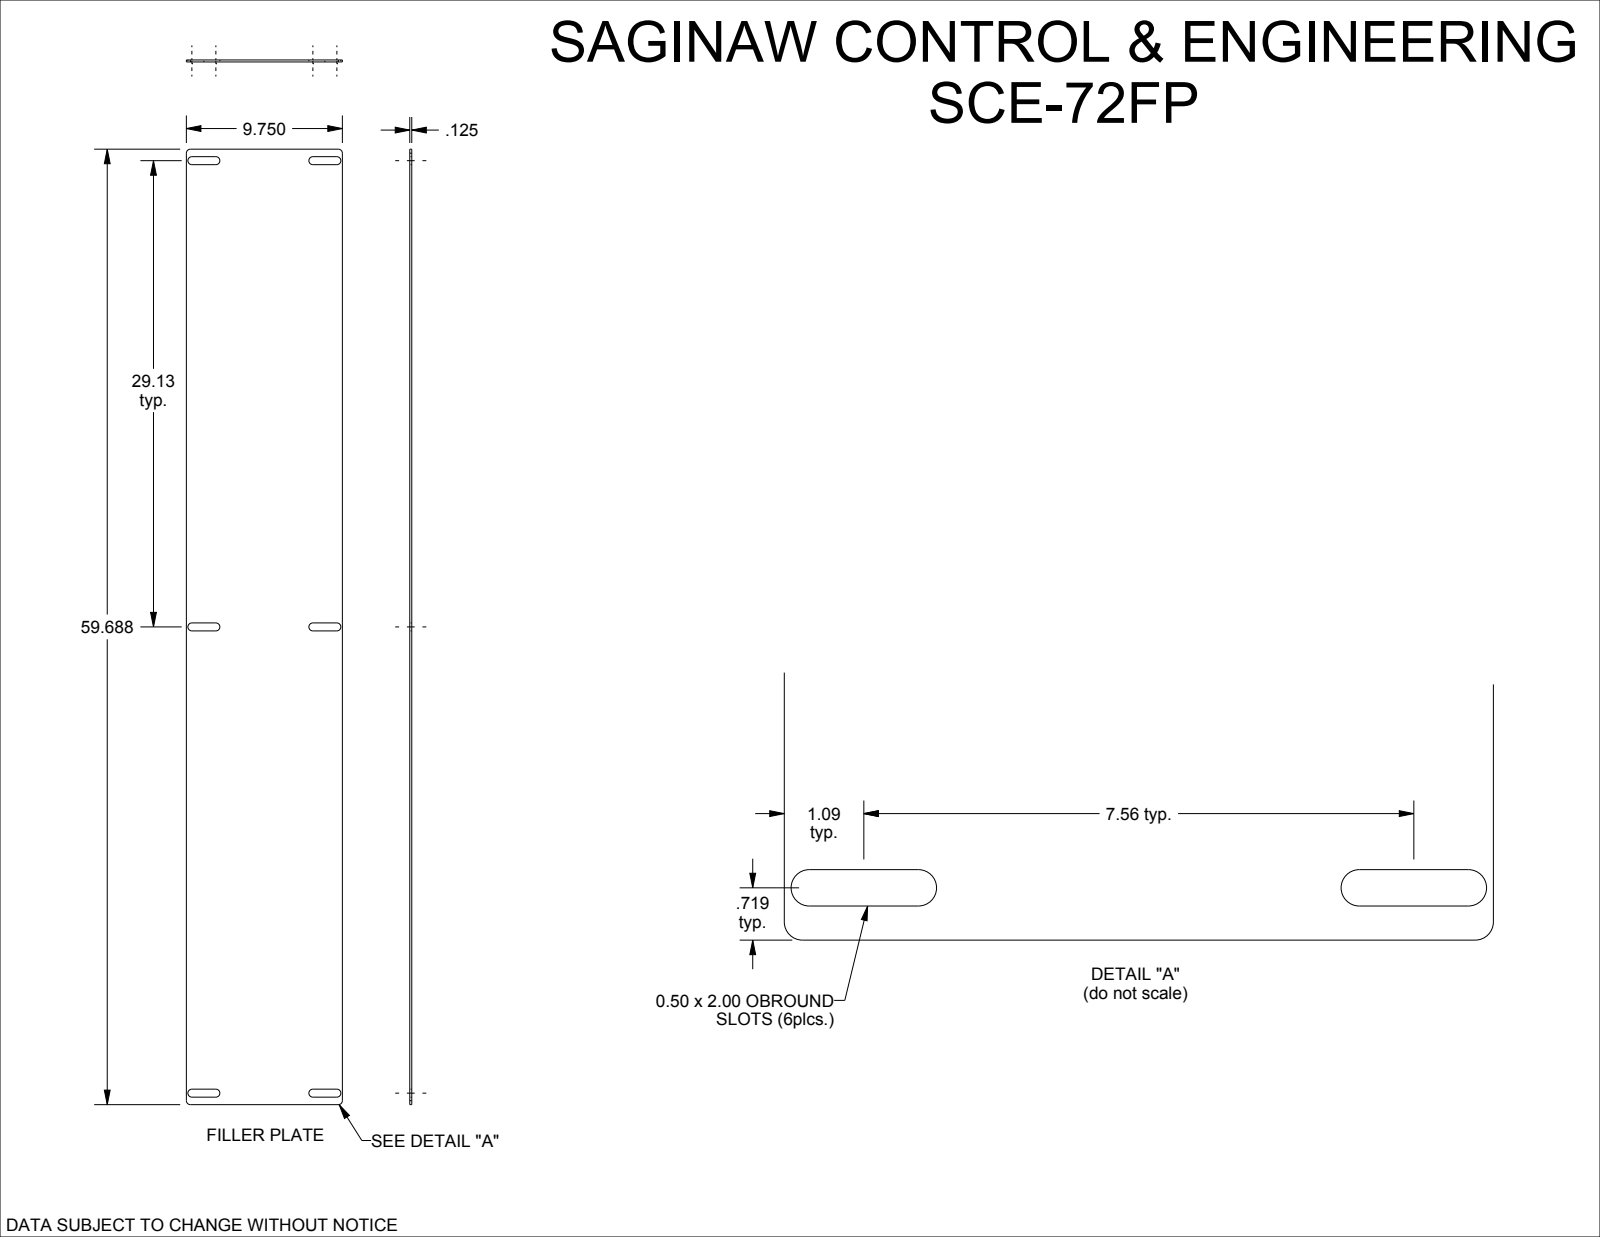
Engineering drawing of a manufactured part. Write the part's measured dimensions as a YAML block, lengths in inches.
part_name: "SCE-72FP"
step_written_by: "SolidWorks 2023 (AUTOMOTIVE_DESIGN)"
units: inches
bodies: {solids: 1, faces: 46, planar: 30, cylindrical: 16, other: 0}
overall_size: [59.687, 9.75, 0.125]
volume: 72.03
surface_area: 1173
partial_cylinders:
  - {radius: 0.25, count: 16}
face_to_face_distances: [0.125, 9.75, 29.125, 59.687, 0.5, 29.594, 30.094, 0.469, 0.969, 58.719]
